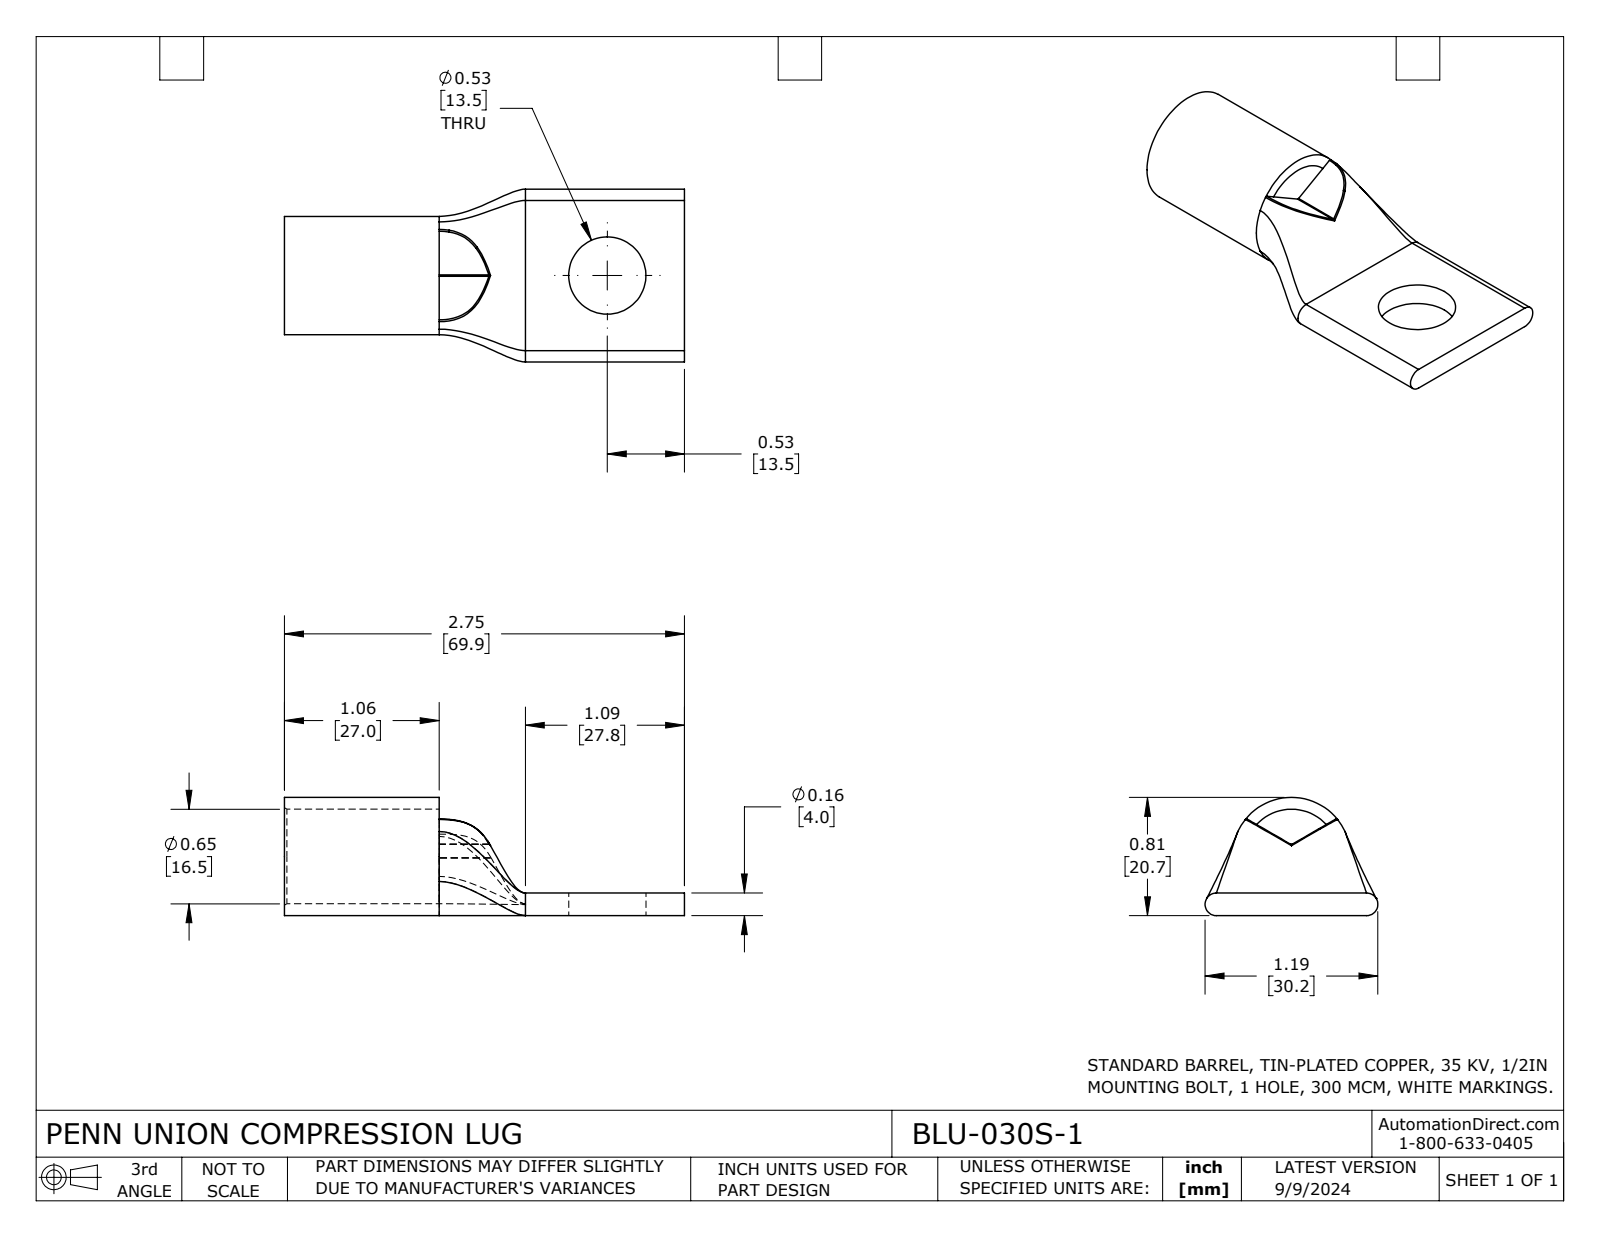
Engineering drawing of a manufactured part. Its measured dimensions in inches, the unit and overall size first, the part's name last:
Units: inches
Overall size (bounding box): 2.75 × 1.188 × 0.813
Round holes (diameter × count): ⌀0.531 ×1, ⌀0.65 ×1
Round bosses / shafts (diameter × count): ⌀0.813 ×1
Partial cylindrical surfaces — rounded edges, fillets, slot ends (radius × count): R0.01 ×2, R0.078 ×2
Main face-to-face distances: 0.156, 0.081, 2.75, 1.063, 1.687, 1.656, 0.593, 1.094
Volume: 0.466 in³ · Surface area: 11.04 in²
Bodies: 1 solid, 37 faces (11 planar, 11 cylindrical, 15 other)
Part name (STEP PRODUCT): BLU-030S-1
STEP written by: SolidWorks 2023 (CONFIG_CONTROL_DESIGN)
